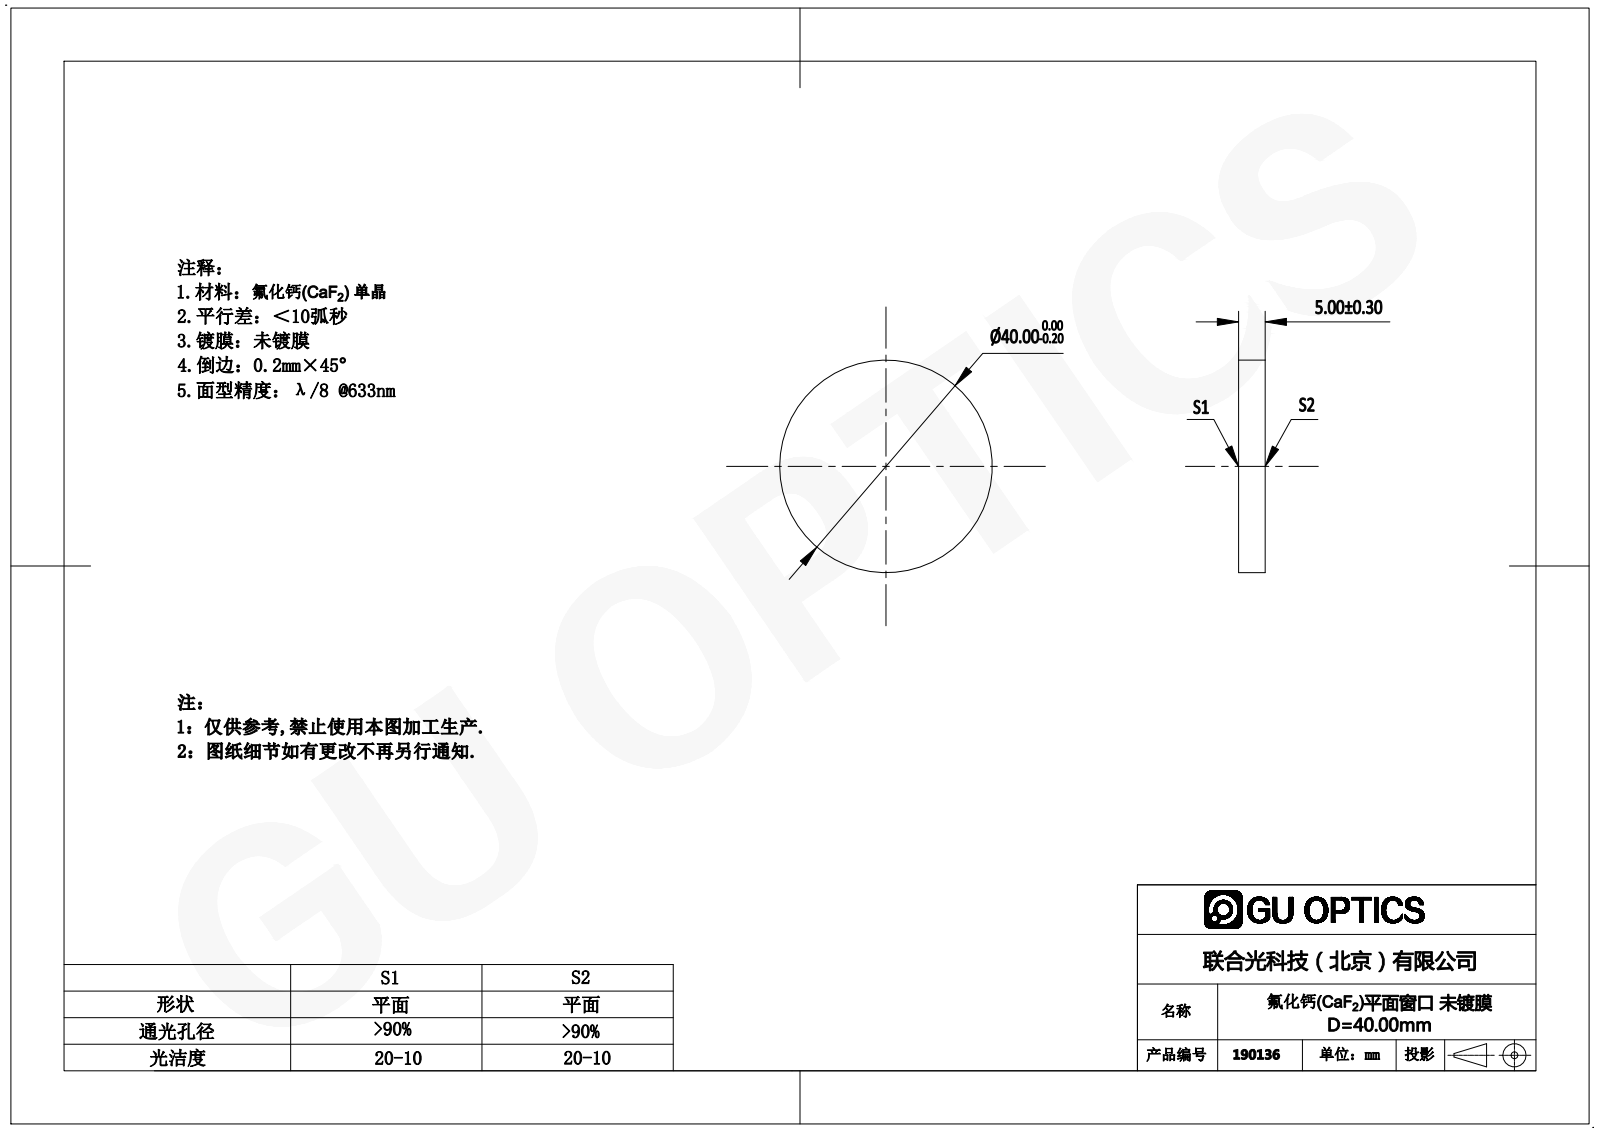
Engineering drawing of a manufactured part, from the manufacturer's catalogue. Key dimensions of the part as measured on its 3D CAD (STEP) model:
Part name (STEP PRODUCT): 190136
STEP written by: SolidWorks 2016 (AUTOMOTIVE_DESIGN)
Units: millimetres
Bodies: 1 solid, 4 faces (2 planar, 2 cylindrical, 0 other)
Overall size (bounding box): 40 × 40 × 5
Volume: 6 283 mm³ · Surface area: 3 142 mm²
Round bosses / shafts (diameter × count): ⌀40 ×1
Main face-to-face distances: 5
